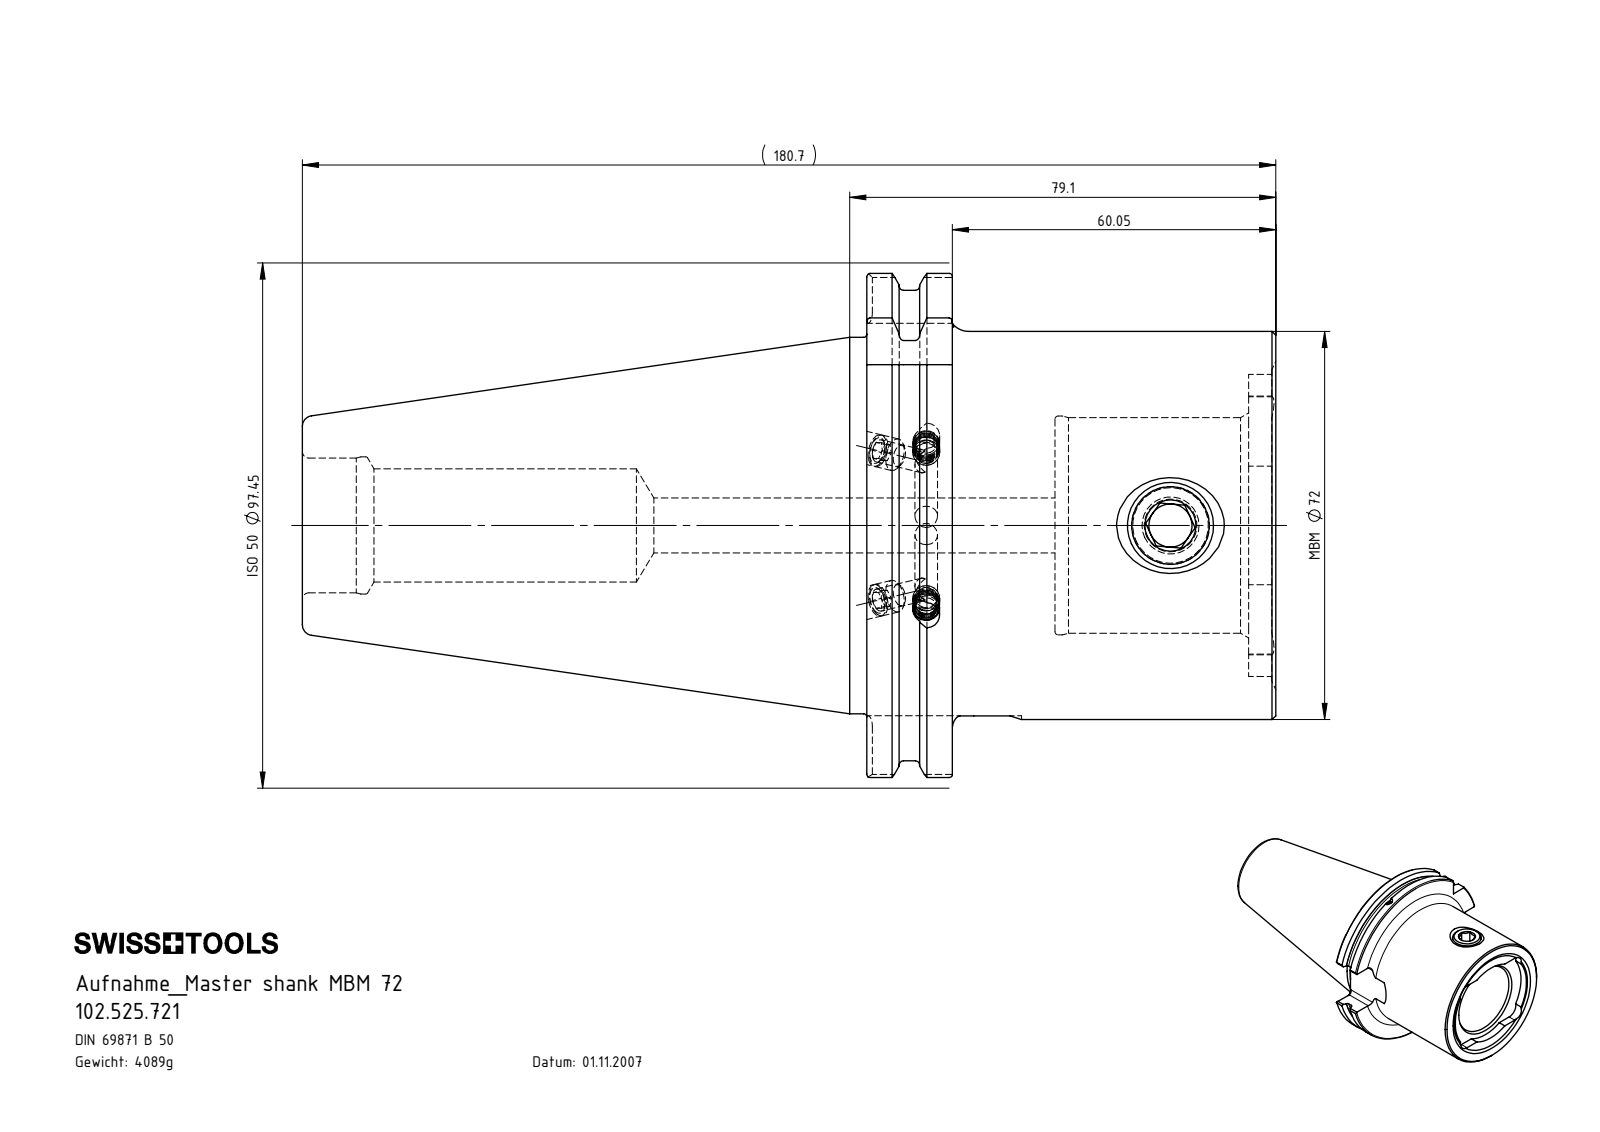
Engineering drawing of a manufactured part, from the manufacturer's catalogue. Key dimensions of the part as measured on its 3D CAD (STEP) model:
Part name (STEP PRODUCT): MB7-ER1.001.022_A; SB5-MB7.K01.079_D_mit Bundkhlung; KVT_MB_600_050; 102.525.721 (+1 more)
STEP written by: SolidWorks 2017 (CONFIG_CONTROL_DESIGN)
Units: millimetres
Bodies: 8 solids, 302 faces (80 planar, 83 cylindrical, 139 other)
Overall size (bounding box): 180.7 × 97.45 × 93.51
Volume: 521 153 mm³ · Surface area: 64 336 mm²
Round holes (diameter × count): ⌀4.2 ×3, ⌀4 ×2, ⌀6 ×2, ⌀5 ×1, ⌀8 ×1, ⌀10.2 ×1, ⌀14.5 ×1, ⌀21 ×1, ⌀25 ×1, ⌀25.45 ×1, ⌀40 ×1, ⌀40.6 ×1
Round bosses / shafts (diameter × count): ⌀91 ×1, ⌀72 ×1, ⌀69.85 ×1, ⌀16 ×1, ⌀5 ×1
Partial cylindrical surfaces — rounded edges, fillets, slot ends (radius × count): R2 ×8, R5.2 ×4, R12.85 ×1, R23.75 ×1, R28.02 ×1, R48.73 ×1
Main face-to-face distances: 15.85, 34.9, 19.05, 75.9, 60.05, 41, 70.85, 55, 35.95, 5.05
